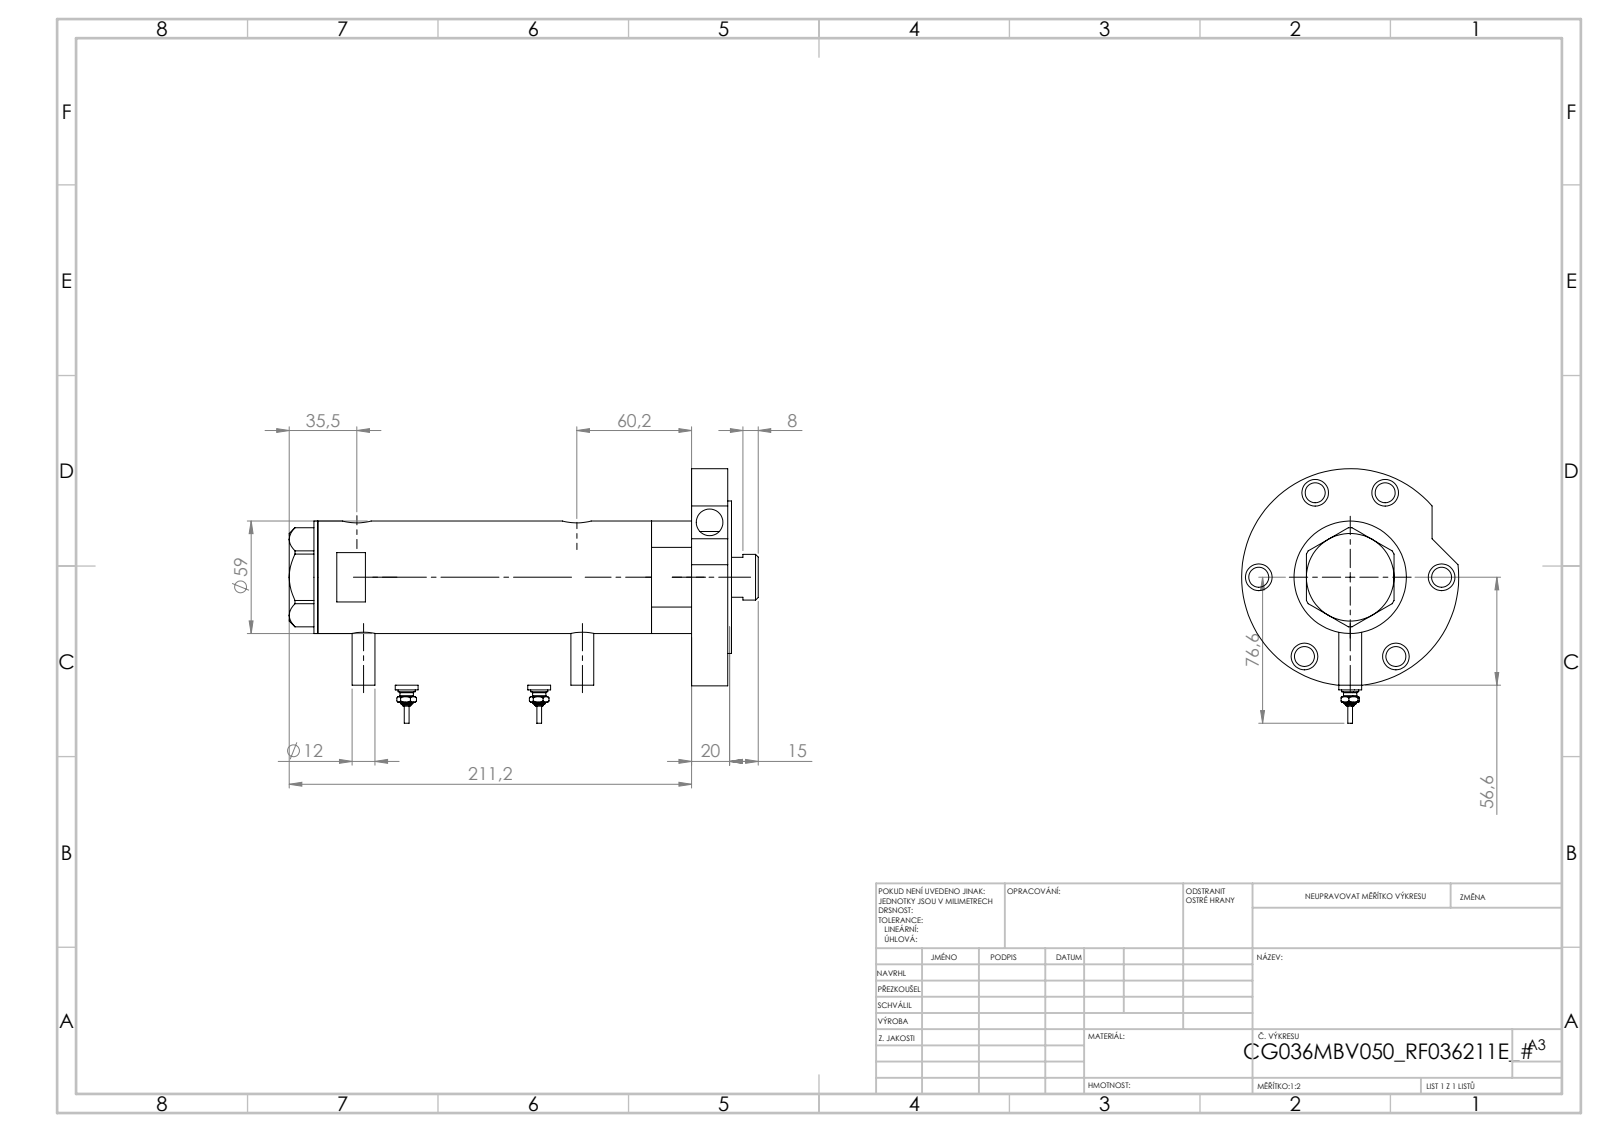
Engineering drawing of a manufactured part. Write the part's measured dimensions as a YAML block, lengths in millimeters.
part_name: "V270CG_BACK; V270CG_MIDDLE; V270CG_VC; V270CG_RF211E (+2 more)"
step_written_by: "SolidWorks 2019 (CONFIG_CONTROL_DESIGN)"
units: millimeters
bodies: {solids: 7, faces: 276, planar: 92, cylindrical: 110, other: 74}
overall_size: [213.42, 118.8, 114]
volume: 620528
surface_area: 136161
round_holes:
  - {diameter: 14, count: 7}
  - {diameter: 10.5, count: 6}
  - {diameter: 5, count: 2}
  - {diameter: 9.73, count: 2}
  - {diameter: 12.5, count: 2}
  - {diameter: 15, count: 2}
  - {diameter: 8.5, count: 1}
  - {diameter: 25, count: 1}
  - {diameter: 26.5, count: 1}
  - {diameter: 36, count: 1}
  - {diameter: 40, count: 1}
  - {diameter: 48, count: 1}
round_bosses_or_shafts:
  - {diameter: 12, count: 3}
  - {diameter: 9, count: 2}
  - {diameter: 7, count: 2}
  - {diameter: 4.34, count: 2}
  - {diameter: 2.4, count: 2}
  - {diameter: 114, count: 1}
  - {diameter: 80, count: 1}
  - {diameter: 59, count: 1}
face_to_face_distances: [19, 2, 21, 137.35, 156.35, 158.35, 107.35, 181.85, 38.5, 175.85]
hole_center_spacings: [48, 2.9, 3.5, 53.34, 79.82, 82.15, 83.14, 85.05]
